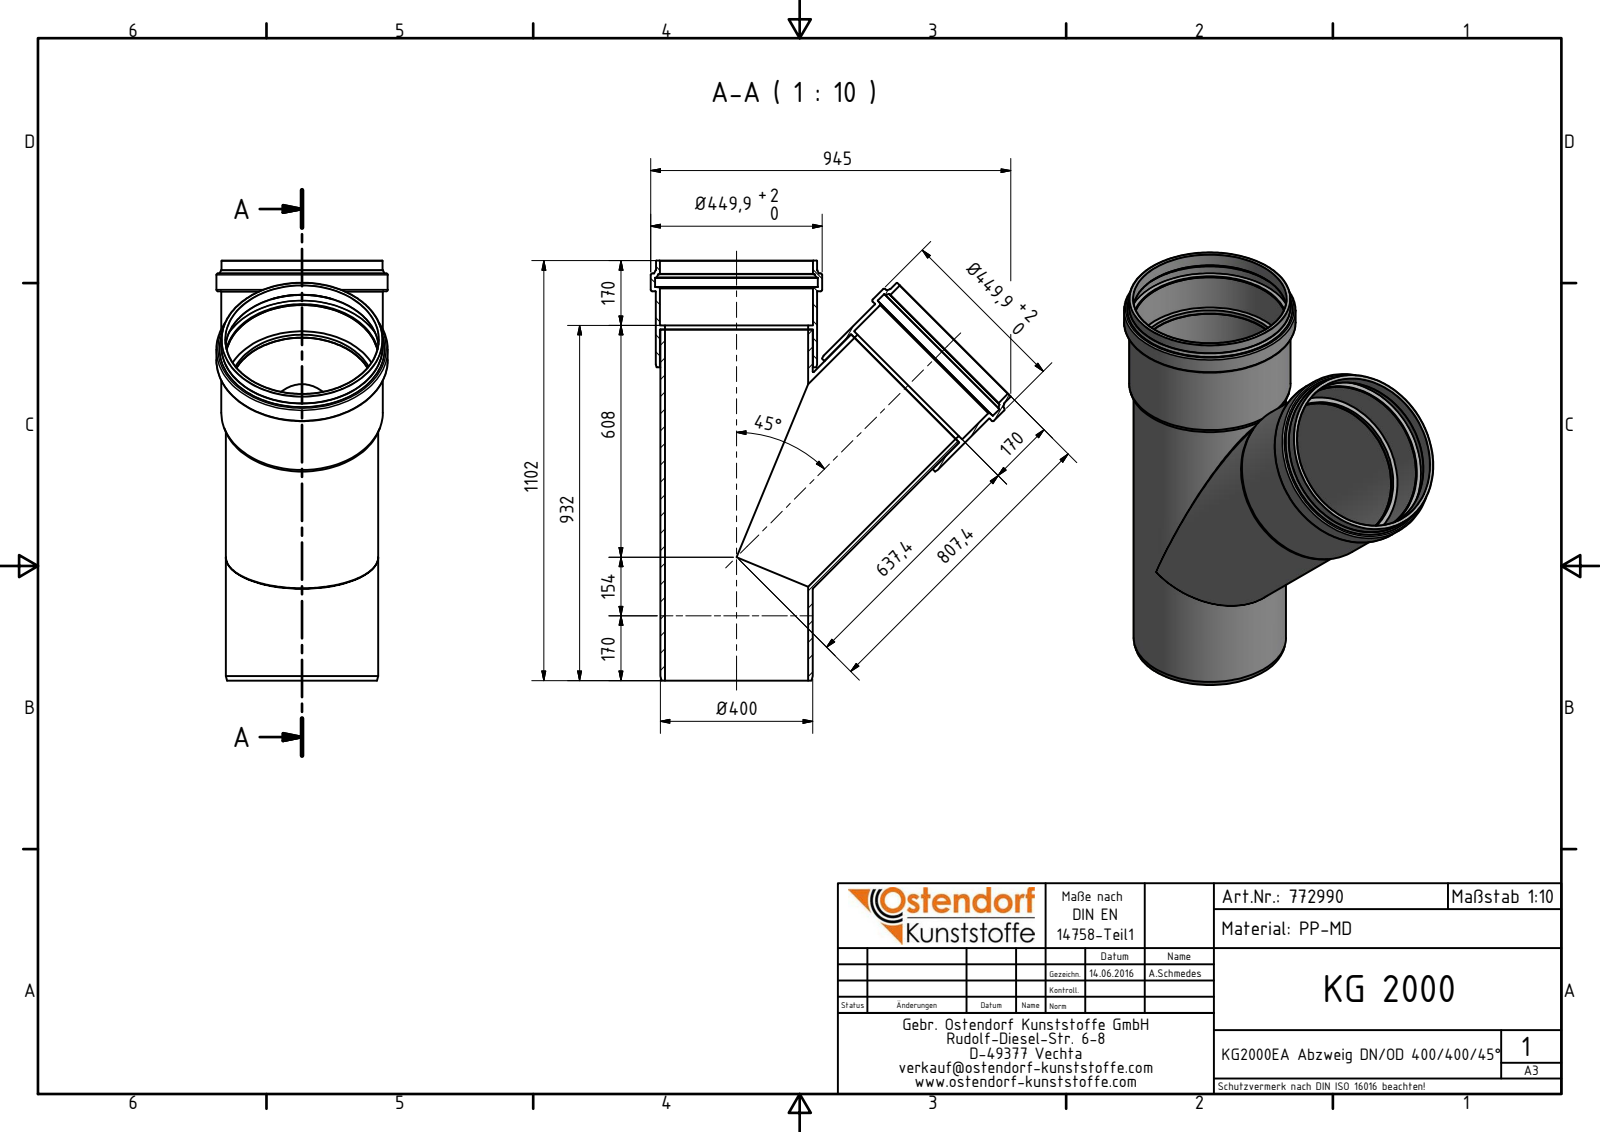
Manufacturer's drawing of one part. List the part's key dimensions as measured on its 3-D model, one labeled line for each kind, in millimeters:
Part name (STEP PRODUCT): 772990 KG2000EA Abzweig DN_OD 400_400; 772990 KG2000EA Abzweig DN_OD 400_400 Teil 2; 772990 KG2000EA Abzweig DN_OD 400_400 Zusammenbau
STEP written by: Autodesk Inventor 2016 (AUTOMOTIVE_DESIGN)
Units: millimetres
Bodies: 3 solids, 82 faces (17 planar, 22 cylindrical, 43 other)
Overall size (bounding box): 1102 × 945 × 449.9
Volume: 26 530 000 mm³ · Surface area: 4 634 000 mm²
Round holes (diameter × count): ⌀376 ×3, ⌀401.7 ×3, ⌀402.1 ×3, ⌀427.7 ×2
Round bosses / shafts (diameter × count): ⌀449.9 ×2, ⌀423.9 ×2, ⌀423.06 ×2, ⌀400 ×2
Main face-to-face distances: 11.1, 98.89, 109.99, 98.9, 110, 46.6, 280, 181.1, 170, 279.96
